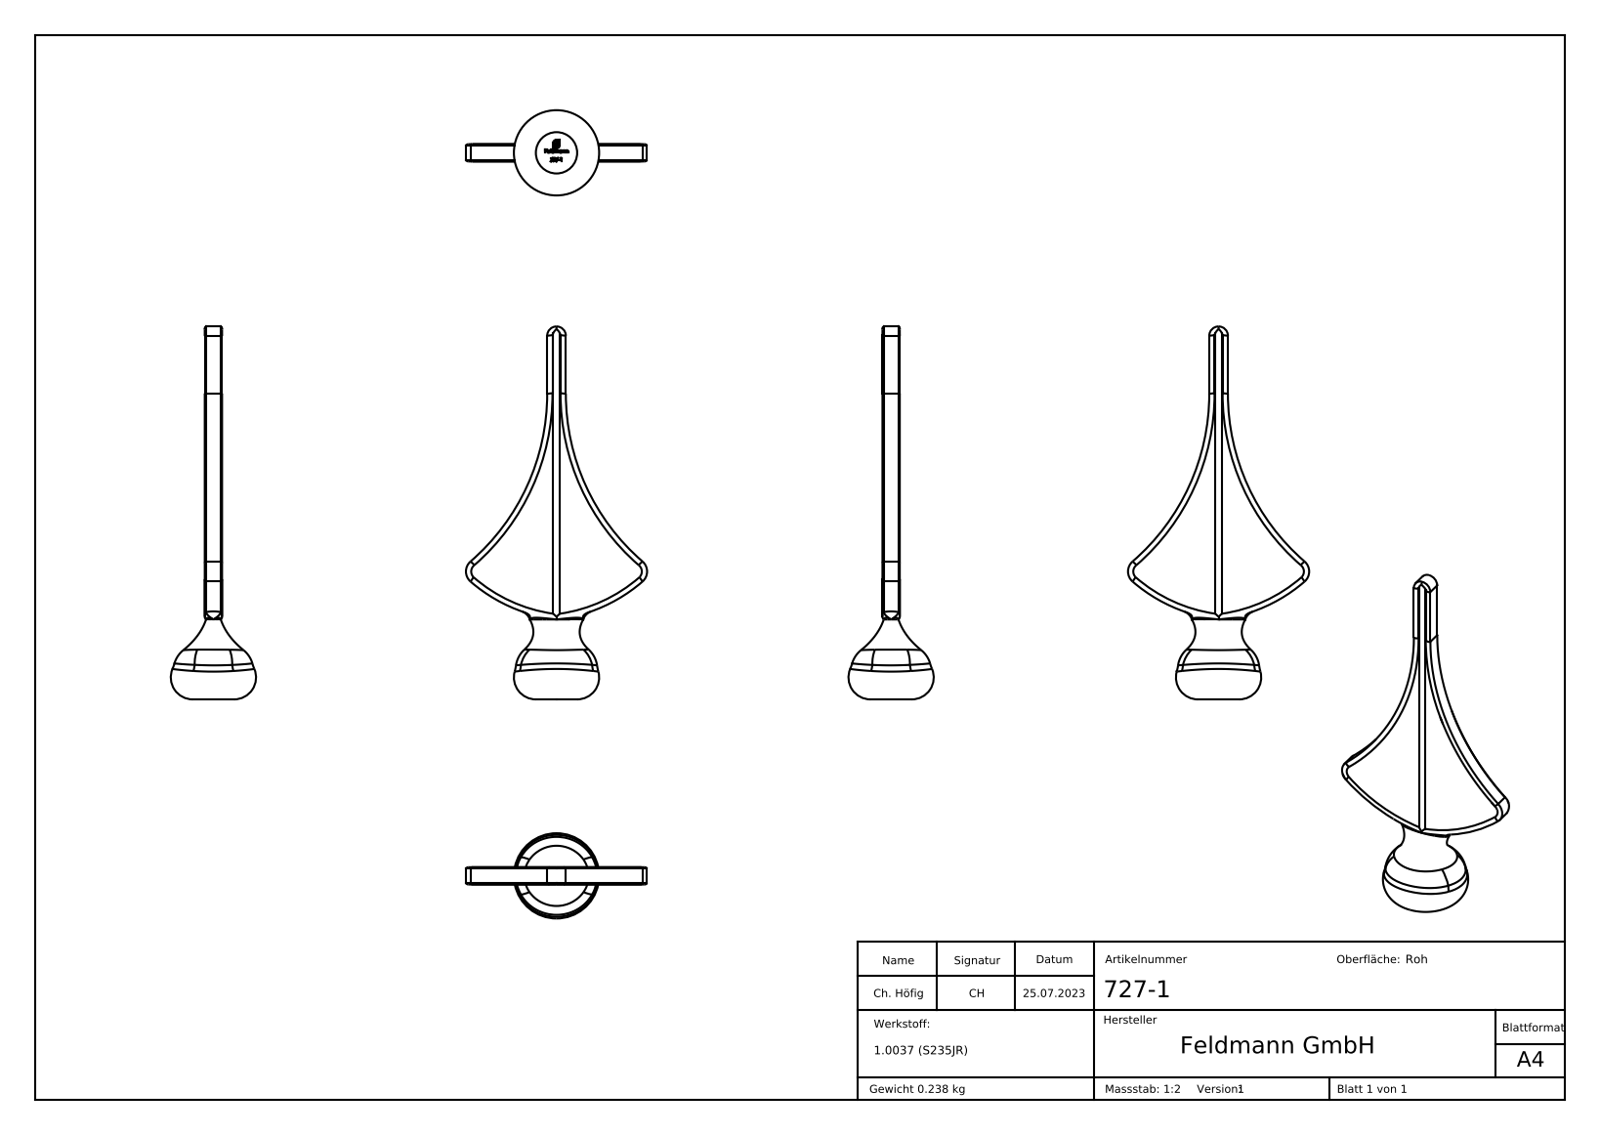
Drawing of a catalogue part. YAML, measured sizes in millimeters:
part_name: "727-1"
step_written_by: "SolidWorks 2018 (CONFIG_CONTROL_DESIGN)"
units: millimeters
bodies: {solids: 1, faces: 247, planar: 128, cylindrical: 9, other: 110}
overall_size: [140, 68, 32]
volume: 30564
surface_area: 10365
partial_cylinders:
  - {radius: 1.81, count: 2}
  - {radius: 5, count: 2}
  - {radius: 60, count: 2}
  - {radius: 83.23, count: 2}
  - {radius: 3.5, count: 1}
face_to_face_distances: [5.5, 7, 2.75, 3.15, 0.58, 4.39, 2.45, 3.21, 1.69, 4.45]
